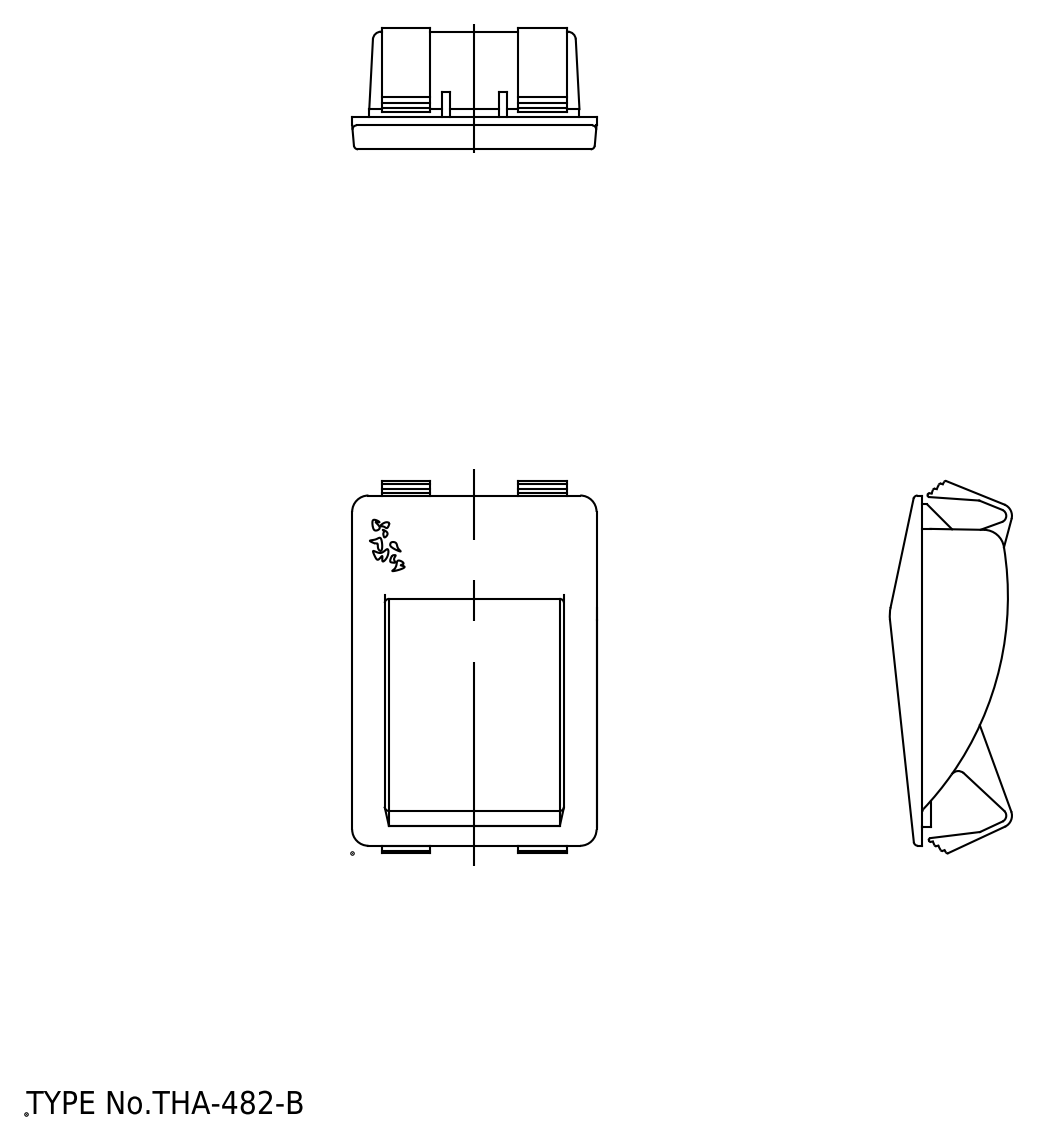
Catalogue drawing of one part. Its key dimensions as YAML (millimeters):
step_written_by: "spGate 16.7.1 (AUTOMOTIVE_DESIGN)"
units: millimeters
bodies: {solids: 1, faces: 208, planar: 88, cylindrical: 86, other: 34}
overall_size: [45.72, 30, 15]
volume: 4130
surface_area: 5859
partial_cylinders:
  - {radius: 0.5, count: 16}
  - {radius: 0.2, count: 10}
  - {radius: 1, count: 6}
  - {radius: 1.5, count: 5}
  - {radius: 2, count: 4}
  - {radius: 0.8, count: 2}
  - {radius: 3, count: 2}
  - {radius: 5, count: 2}
face_to_face_distances: [2.4, 16.8, 6, 9.6, 20.4, 3.6, 26.4, 1, 30, 5]
